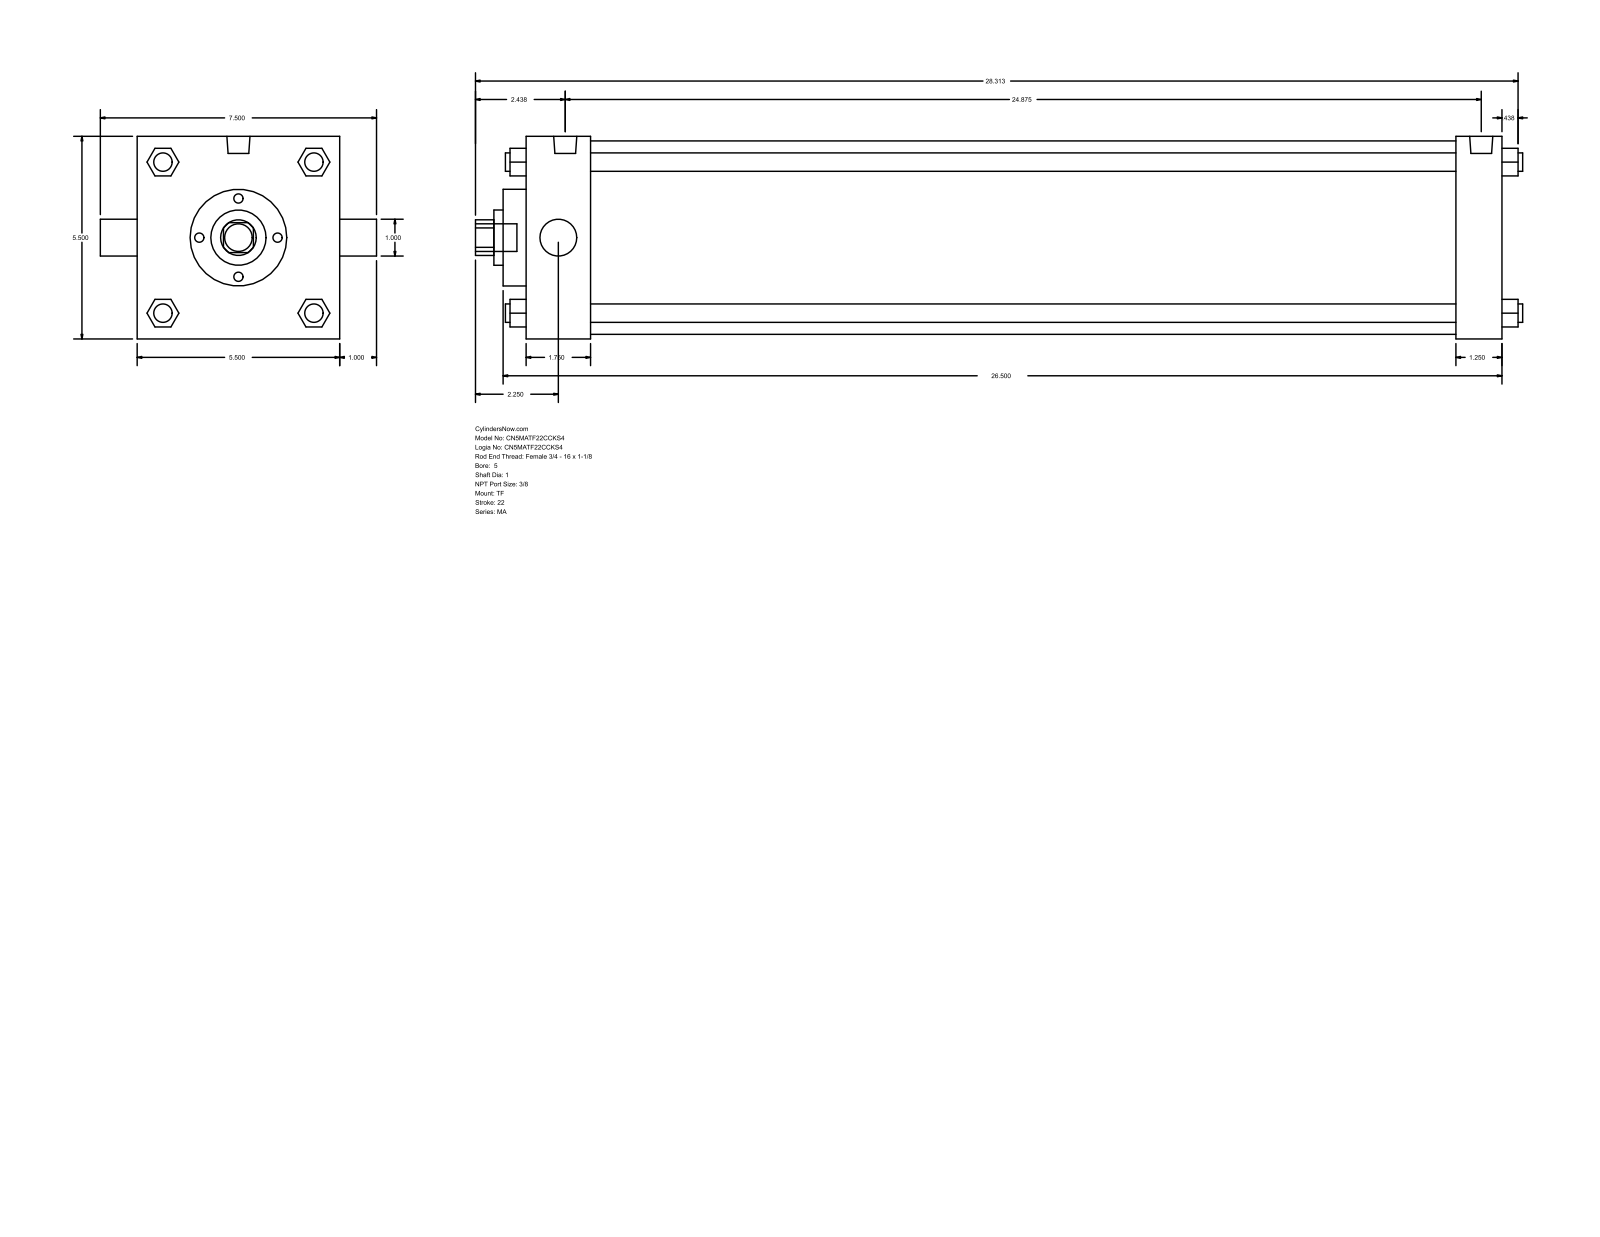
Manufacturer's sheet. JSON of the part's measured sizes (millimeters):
{"part_name": "MA_TF__0500_1", "step_written_by": "GSSL Pune (CONFIG_CONTROL_DESIGN)", "units": "millimeters", "bodies": {"solids": 0, "faces": 122, "planar": 93, "cylindrical": 29, "other": 0}, "overall_size": [722.31, 190.5, 139.7], "round_holes": [[25.4, 2], [38.1, 1], [66.67, 1], [133.35, 1]], "round_bosses_or_shafts": [[12.7, 4], [11.11, 3], [15.93, 2], [19.05, 1]], "partial_cylinders_radius": [[12.29, 1]], "face_to_face_distances": [139.7, 673.1, 641.35, 31.75, 44.46, 596.89, 628.64, 15.87, 60.33, 657.22]}
